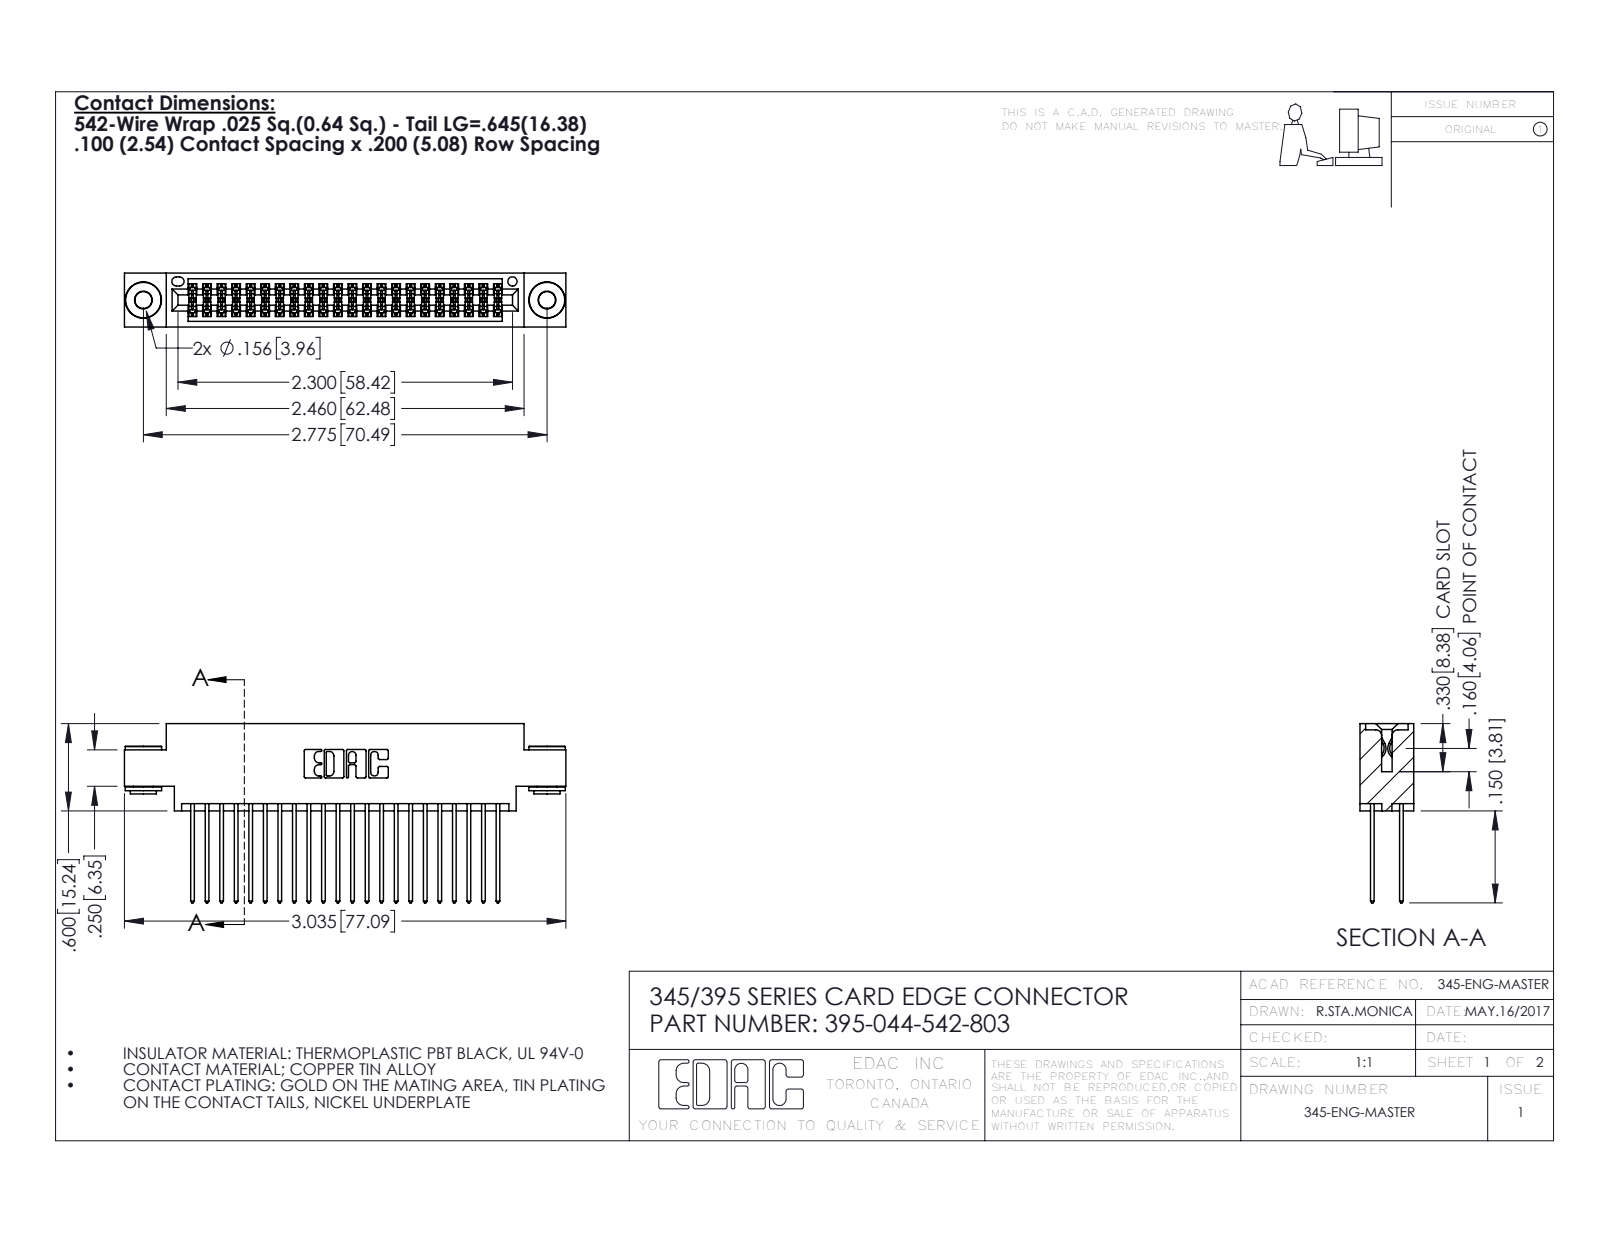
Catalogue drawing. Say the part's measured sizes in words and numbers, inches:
The part is named "395-044-542-803; 345-292-001_345-293-142; 345 Part_0.170 Offset - 0.156 Dia-TH; 345-250-002_345-250-002-102". Its 3-D file was written by "SolidWorks 2016 (CONFIG_CONTROL_DESIGN)". It is 47 solids with 2368 faces: 1546 planar, 814 cylindrical and 8 other. Overall it measures 3.035 by 1.232 by 0.37 inches. Its volume is 0.452 cubic inches and its surface area 18.41 square inches. Round holes: 2 of diameter 0.116, 2 of diameter 0.156, 1 of diameter 0.064. Round bosses or shafts: 2 of diameter 0.25, 2 of diameter 0.18, 2 of diameter 0.136. Partial cylindrical surfaces (rounded edges, fillets, slot ends): 66 of radius 0.006, 44 of radius 0.01, 22 of radius 0.01, 6 of radius 0.007, 6 of radius 0.031, 3 of radius 0.026, 2 of radius 0.014, 2 of radius 0.019. The main face-to-face distances are 0.072, 0.298, 0.2, 0.098, 0.272, 0.025, 0.37, 0.225, 0.175, 0.1. The hole center spacings are 0.27, 2.541, 2.775.
